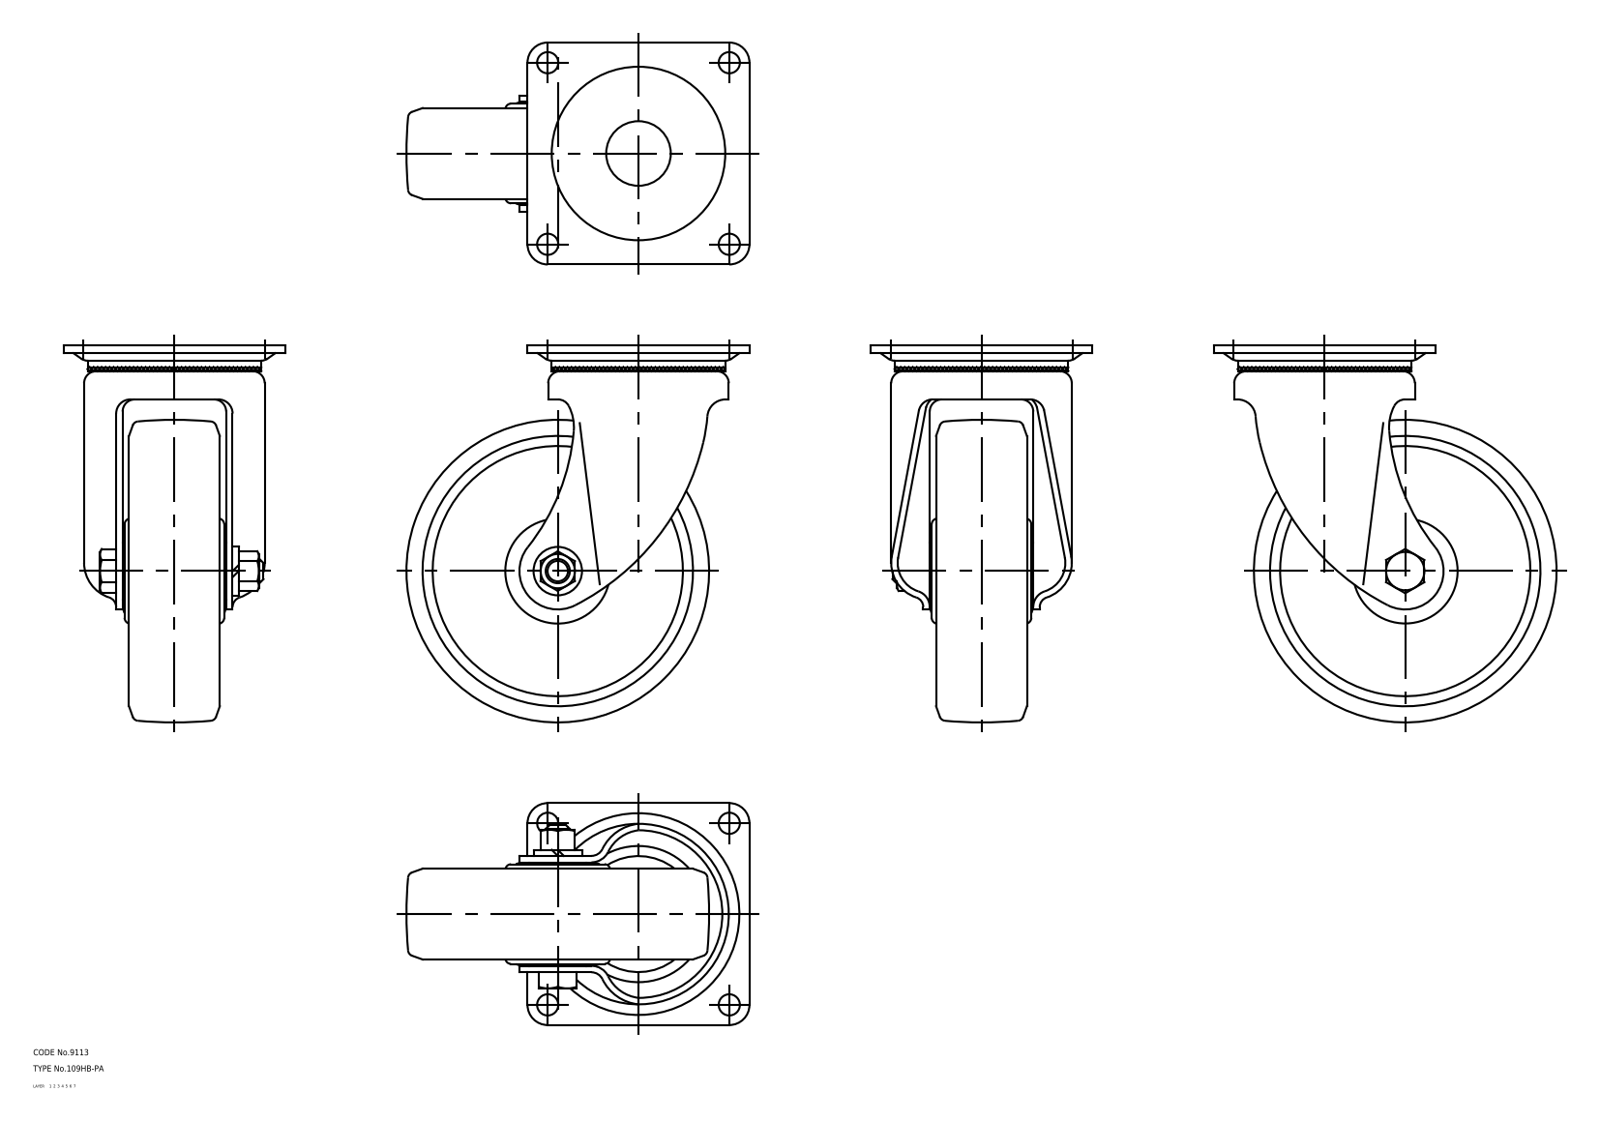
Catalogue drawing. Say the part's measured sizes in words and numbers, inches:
The part is named "67126167; 67126180; 67126193; 67126206 (+1 more)". Its 3-D file was written by "CADfix (AUTOMOTIVE_DESIGN)". It is 5 solids with 249 faces: 0 planar, 0 cylindrical and 249 other. Overall it measures 7.362 by 6.693 by 4.331 inches. Its volume is 52.17 cubic inches and its surface area 231 square inches.
